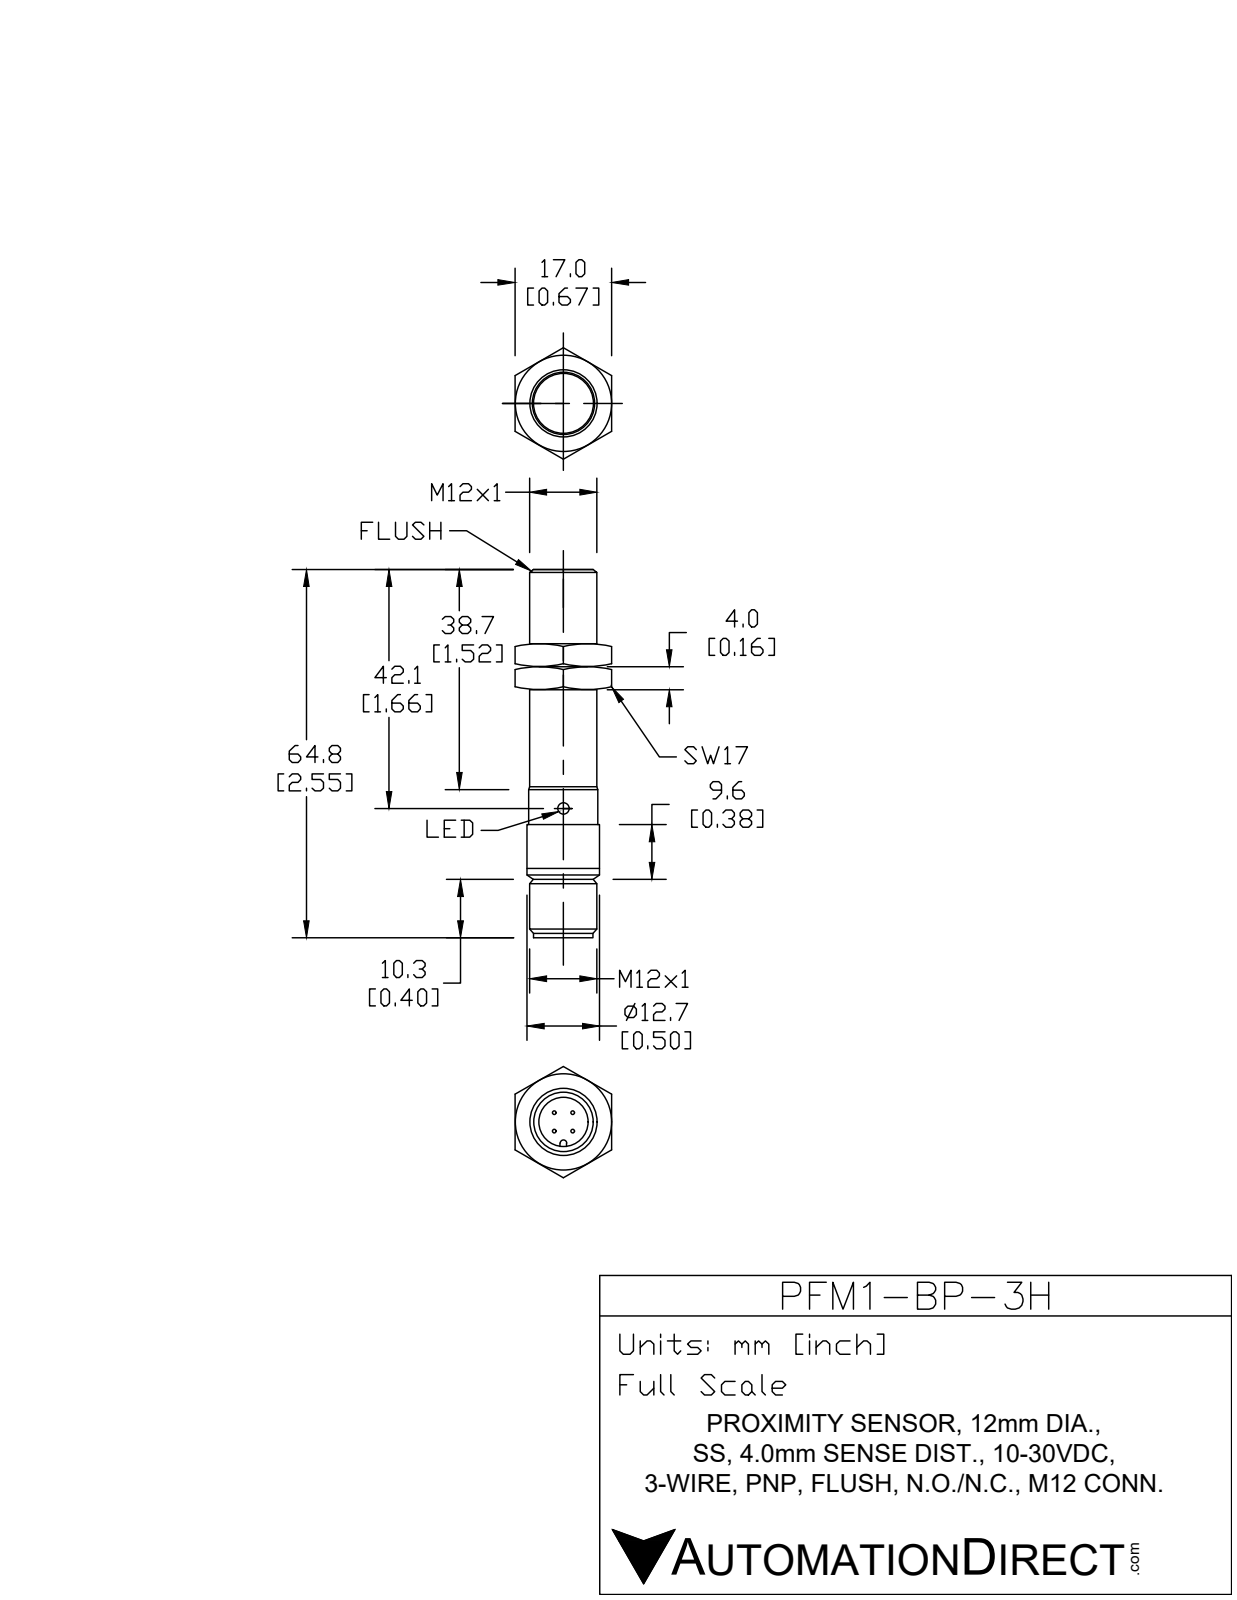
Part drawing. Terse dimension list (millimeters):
name: PFM1-BP-3H
written by: SolidWorks 2017 (AUTOMOTIVE_DESIGN)
unit: mm
bodies: 3 solids, 70 faces (10 planar, 36 cylindrical, 24 other)
size: 64.6 × 12.7 × 12.7
volume: 6 920 mm³; area: 3 948 mm²
holes: 1× ⌀3, 1× ⌀8.4, 1× ⌀8.5, 1× ⌀9.5
bosses: 4× ⌀1, 1× ⌀12.7, 1× ⌀12, 1× ⌀10.5, 1× ⌀10.1, 1× ⌀9.4
rounds: 1× R0.6, 1× R5.6
face distances: 1.8, 52.7, 54.5, 55.7, 3, 1.2, 63.6, 10.9, 9.1, 7.9
